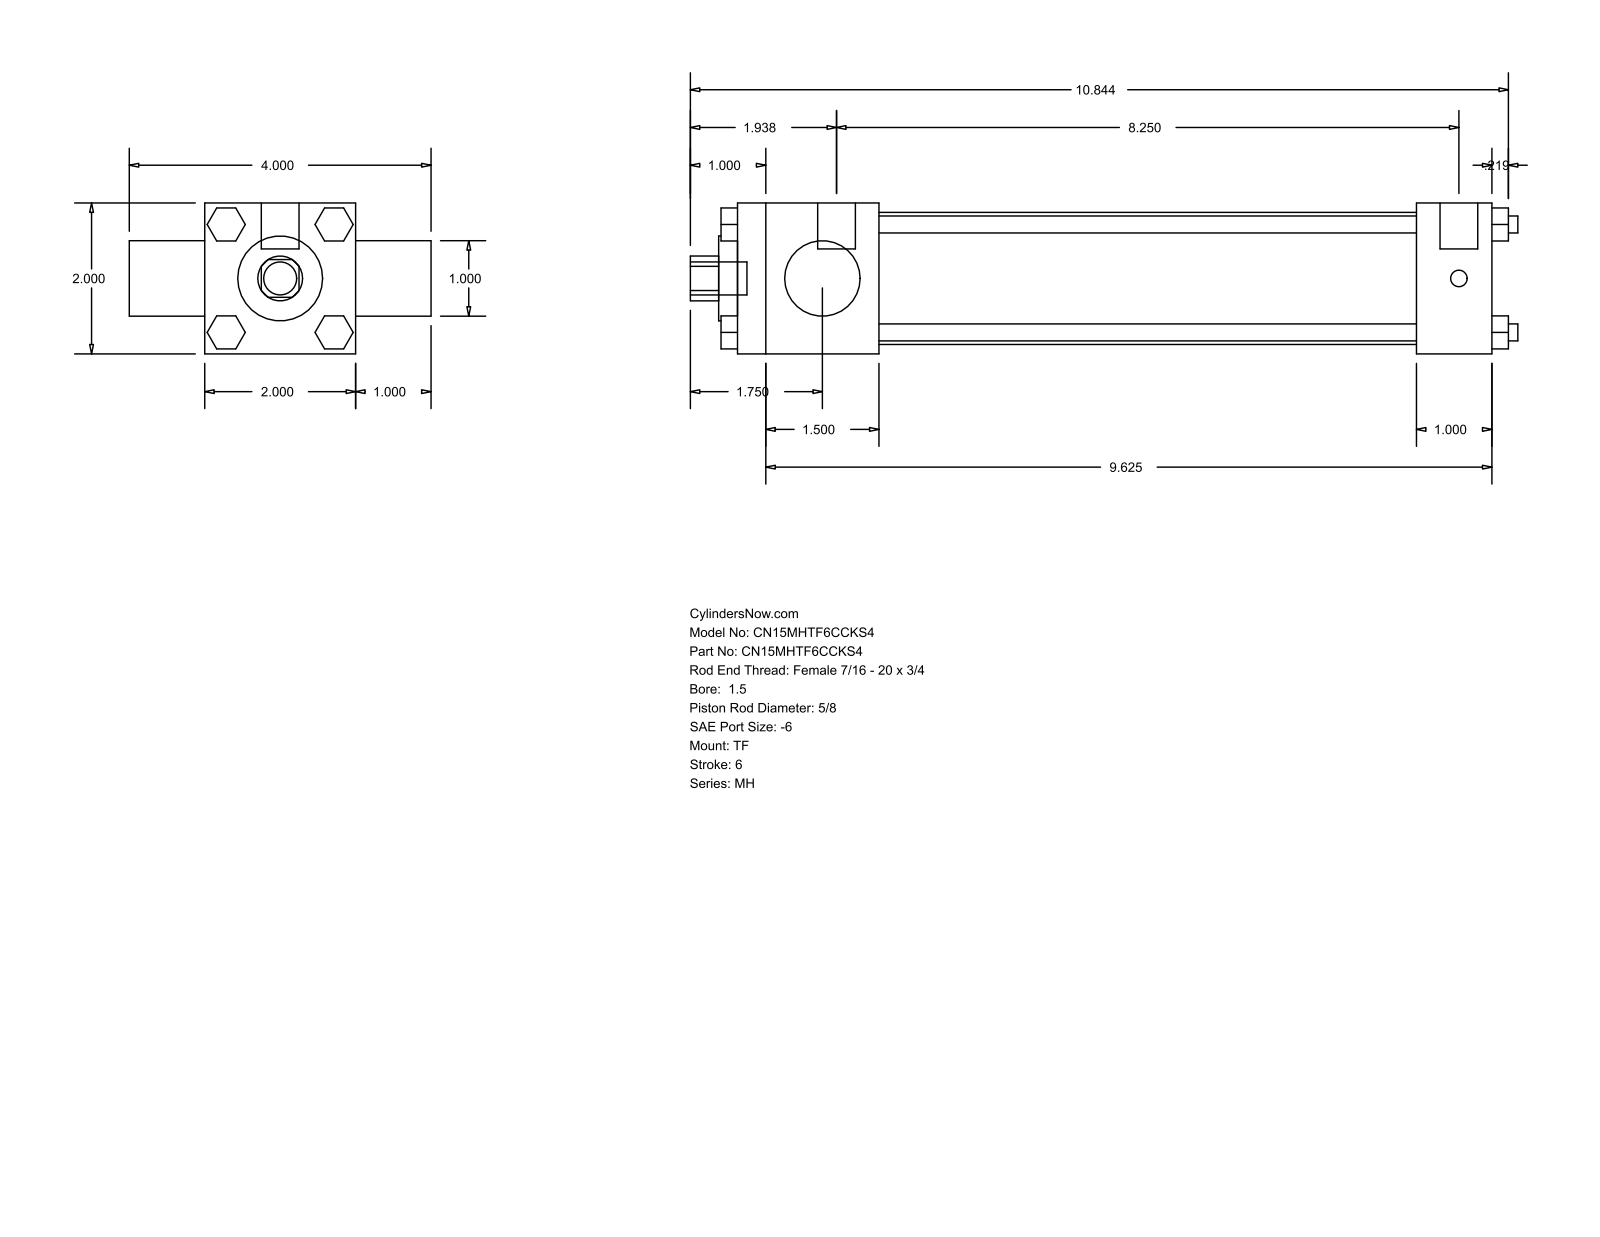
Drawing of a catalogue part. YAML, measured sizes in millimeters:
part_name: "MH_TF__0150_0.625"
step_written_by: "GSSL Pune (CONFIG_CONTROL_DESIGN)"
units: millimeters
bodies: {solids: 0, faces: 120, planar: 92, cylindrical: 28, other: 0}
overall_size: [278.61, 101.6, 50.8]
round_holes:
  - {diameter: 15.88, count: 1}
  - {diameter: 25.4, count: 1}
  - {diameter: 28.57, count: 1}
  - {diameter: 44.45, count: 1}
round_bosses_or_shafts:
  - {diameter: 5.71, count: 4}
  - {diameter: 5.56, count: 3}
  - {diameter: 12.7, count: 2}
  - {diameter: 11.11, count: 1}
partial_cylinders:
  - {radius: 7.54, count: 1}
face_to_face_distances: [50.8, 254, 25.4, 76.2, 47.62, 206.38, 228.59, 180.97, 25.41, 11.11]
